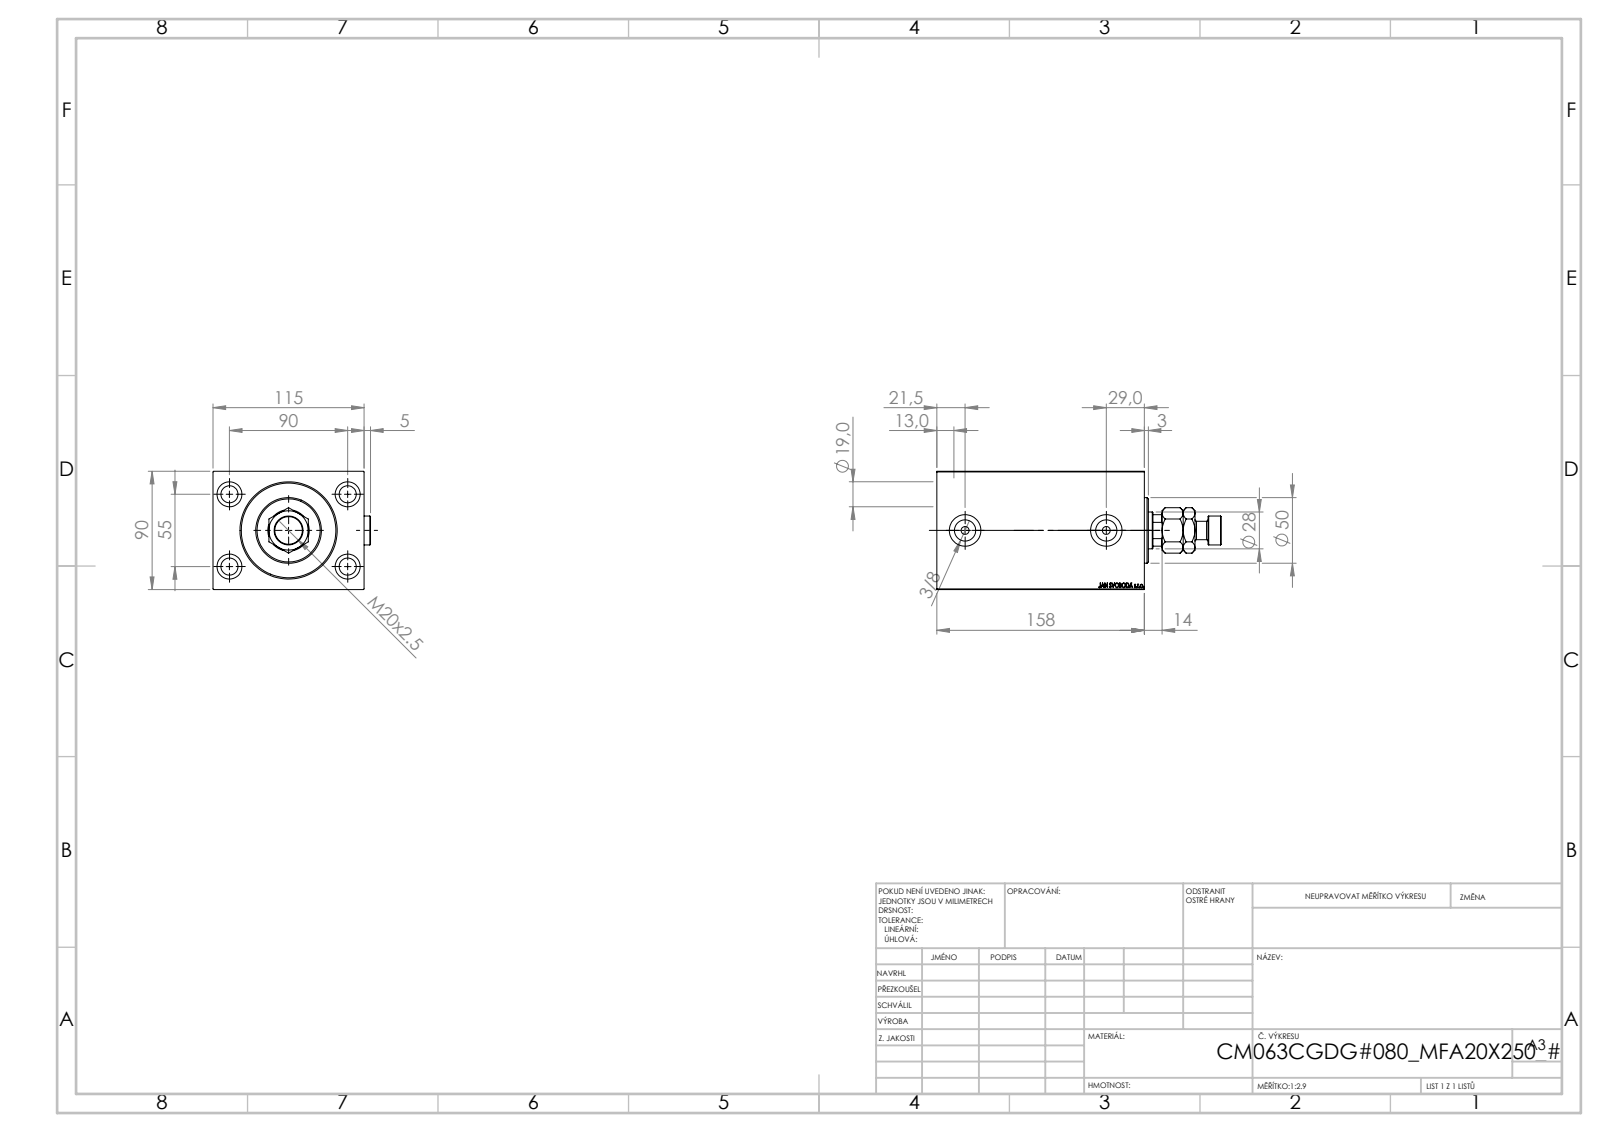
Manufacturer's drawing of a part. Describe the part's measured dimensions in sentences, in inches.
The part is named "V450CM_C_Body; V450CM_C_VCP; Zatka_OIL_PORT; V450CM_VC_B (+1 more)". Its 3-D file was written by "SolidWorks 2019 (CONFIG_CONTROL_DESIGN)". It is 6 solids with 971 faces: 459 planar, 82 cylindrical and 430 other. Overall it measures 8.524 by 4.72 by 3.543 inches. Its volume is 82.69 cubic inches and its surface area 293.5 square inches. Round holes: 4 of diameter 0.512, 4 of diameter 0.748, 2 of diameter 0.236, 2 of diameter 0.637, 2 of diameter 0.945, 1 of diameter 0.728, 1 of diameter 1.102, 1 of diameter 1.24, 1 of diameter 2.48, 1 of diameter 2.559, 1 of diameter 2.835. Round bosses or shafts: 3 of diameter 0.866, 1 of diameter 1.969, 1 of diameter 0.551. Partial cylindrical surfaces (rounded edges, fillets, slot ends): 1 of radius 0.531. The main face-to-face distances are 3.543, 4.528, 6.22, 0.689, 5.531, 0.531, 5, 5.689, 1.85, 2.539. The hole center spacings are 2.076, 2.165, 3.543, 4.153, 4.232.
